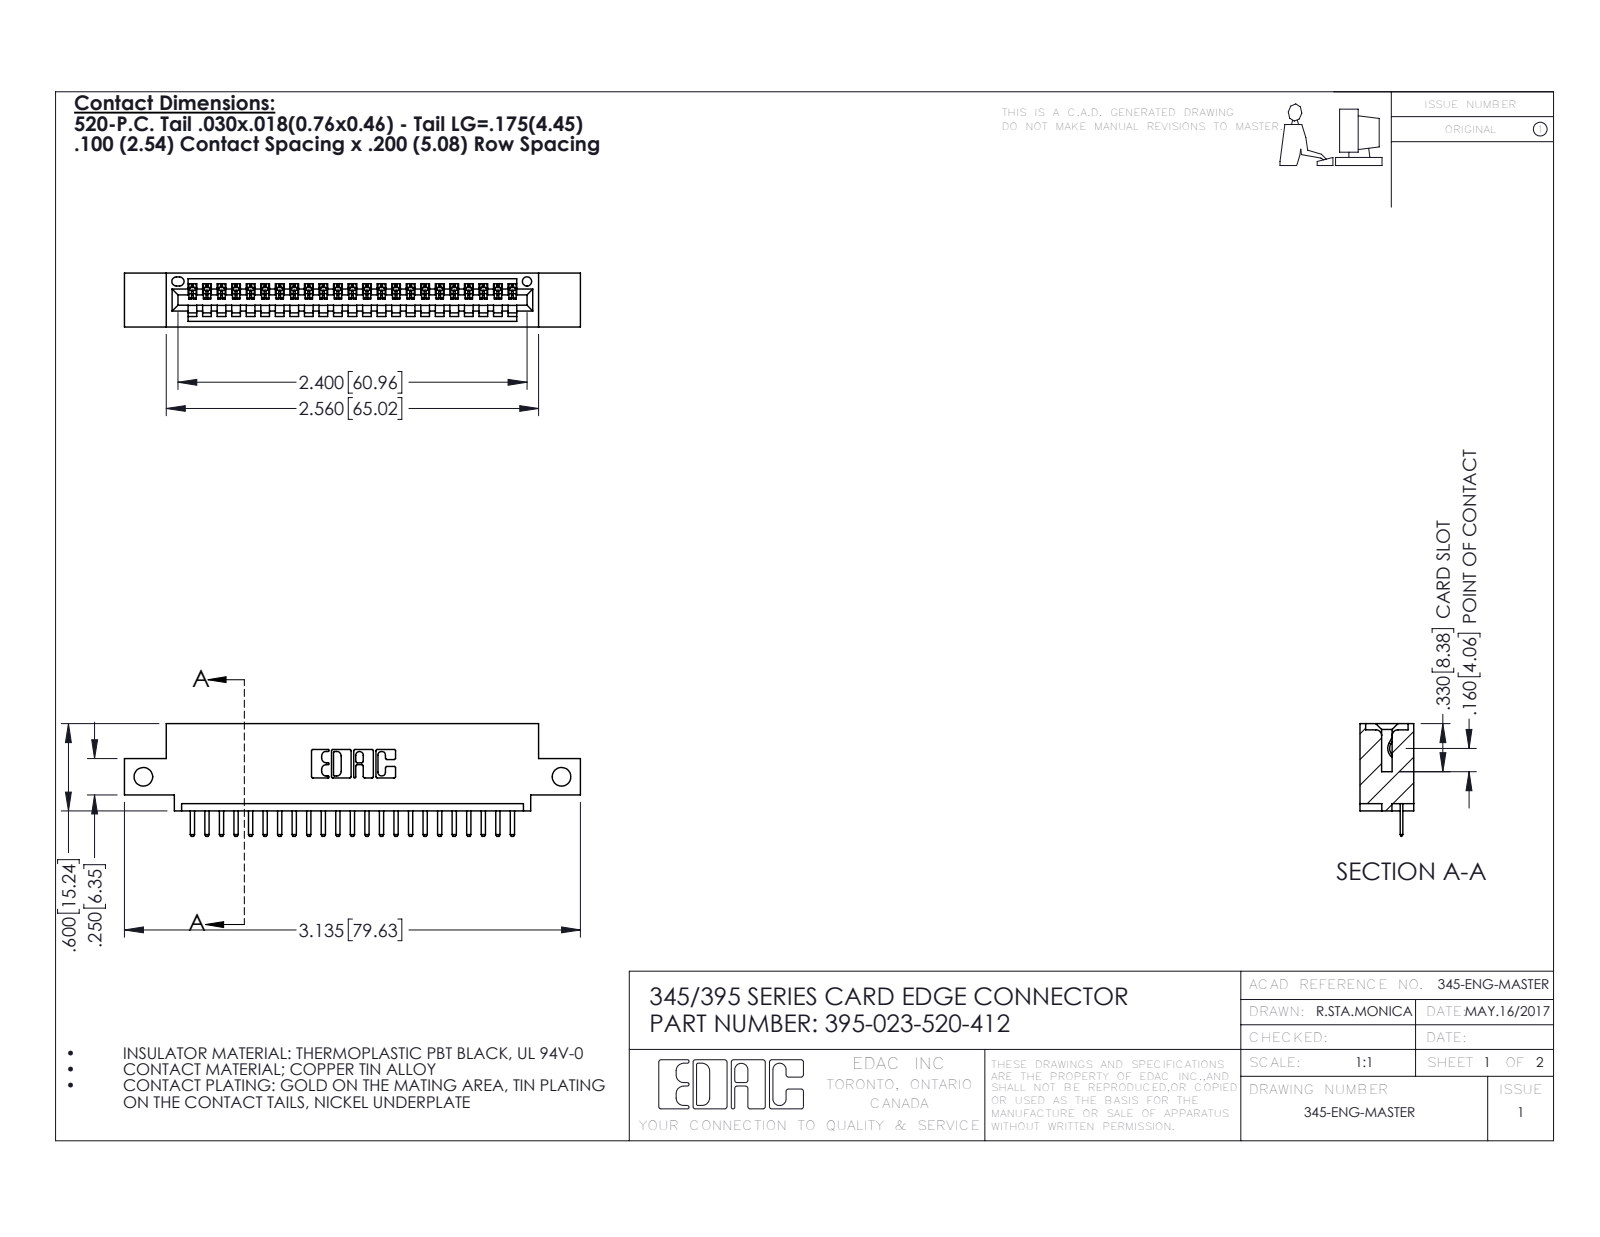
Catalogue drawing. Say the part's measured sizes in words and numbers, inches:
The part is named "345 Part_0.110 Offset - Side Mount; 395-023-520-412; 345-292-001_345-293-120". Its 3-D file was written by "SolidWorks 2016 (CONFIG_CONTROL_DESIGN)". It is 24 solids with 1556 faces: 1050 planar, 506 cylindrical and 0 other. Overall it measures 3.135 by 0.775 by 0.37 inches. Its volume is 0.438 cubic inches and its surface area 13.96 square inches. Round holes: 2 of diameter 0.128, 1 of diameter 0.064. Partial cylindrical surfaces (rounded edges, fillets, slot ends): 48 of radius 0.01, 46 of radius 0.006, 22 of radius 0.01, 6 of radius 0.007, 6 of radius 0.031, 3 of radius 0.026, 2 of radius 0.031, 2 of radius 0.04. The main face-to-face distances are 0.072, 0.298, 0.37, 0.2, 0.098, 0.272, 0.025, 0.225, 0.072, 0.149. The hole center spacings are 2.875.
